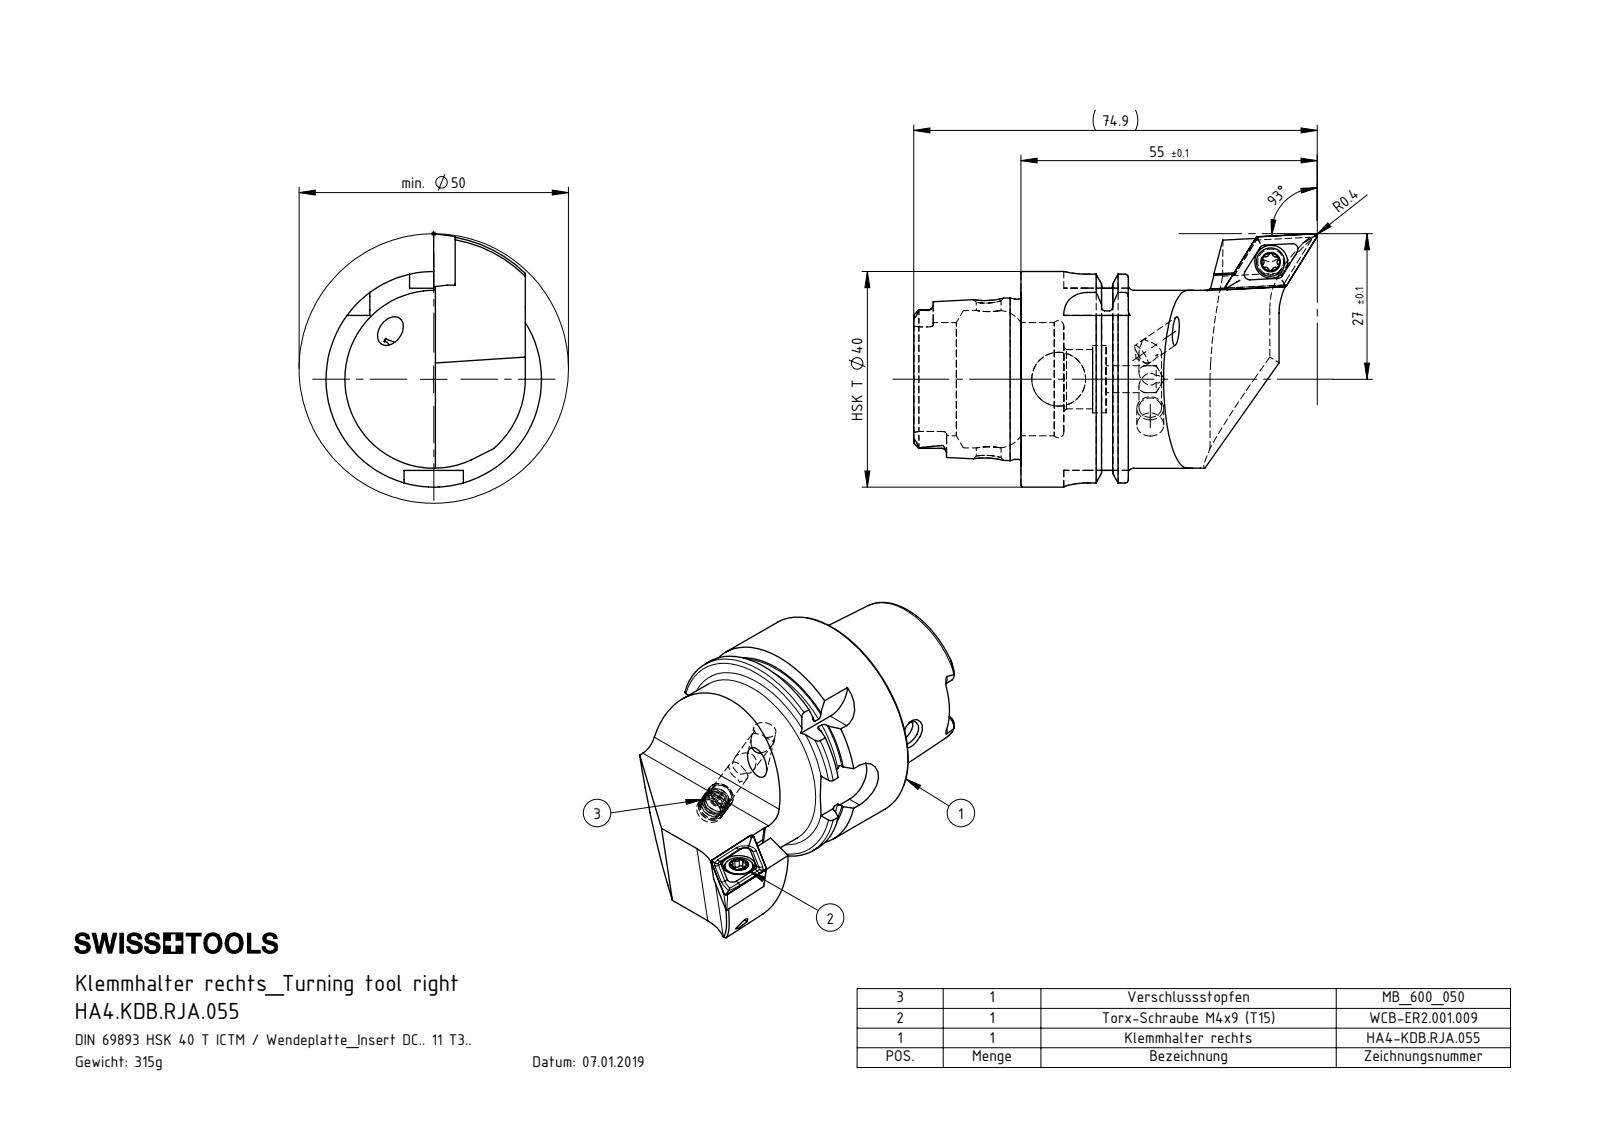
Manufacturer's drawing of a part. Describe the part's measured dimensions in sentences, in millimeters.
The part is named "WCB-ER2.001.009_A; HA4.KDB.RJA.055; DCMT11T304; KVT_MB_600_050 (+1 more)". Its 3-D file was written by "SolidWorks 2015 (AUTOMOTIVE_DESIGN)". It is 5 solids with 314 faces: 79 planar, 91 cylindrical and 144 other. Overall it measures 74.91 by 47 by 40 millimeters. Its volume is 39 831 cubic millimeters and its surface area 13 616 square millimeters. Round holes: 2 of diameter 4.2, 2 of diameter 5, 1 of diameter 3.3, 1 of diameter 4, 1 of diameter 4.4, 1 of diameter 4.6, 1 of diameter 6.1, 1 of diameter 10, 1 of diameter 11, 1 of diameter 12.5, 1 of diameter 21, 1 of diameter 25.5. Round bosses or shafts: 1 of diameter 40, 1 of diameter 34.75, 1 of diameter 33, 1 of diameter 29.71, 1 of diameter 5.25, 1 of diameter 5, 1 of diameter 4. Partial cylindrical surfaces (rounded edges, fillets, slot ends): 6 of radius 0.34, 6 of radius 0.59, 6 of radius 0.9, 4 of radius 4.5, 2 of radius 1.82, 2 of radius 1.88, 1 of radius 3, 1 of radius 11. The main face-to-face distances are 7.95, 16.7, 19.95, 12, 13.03, 3.67, 19.9, 27.85, 39.85, 35.7. The hole center spacings are 44.96, 45.08.
